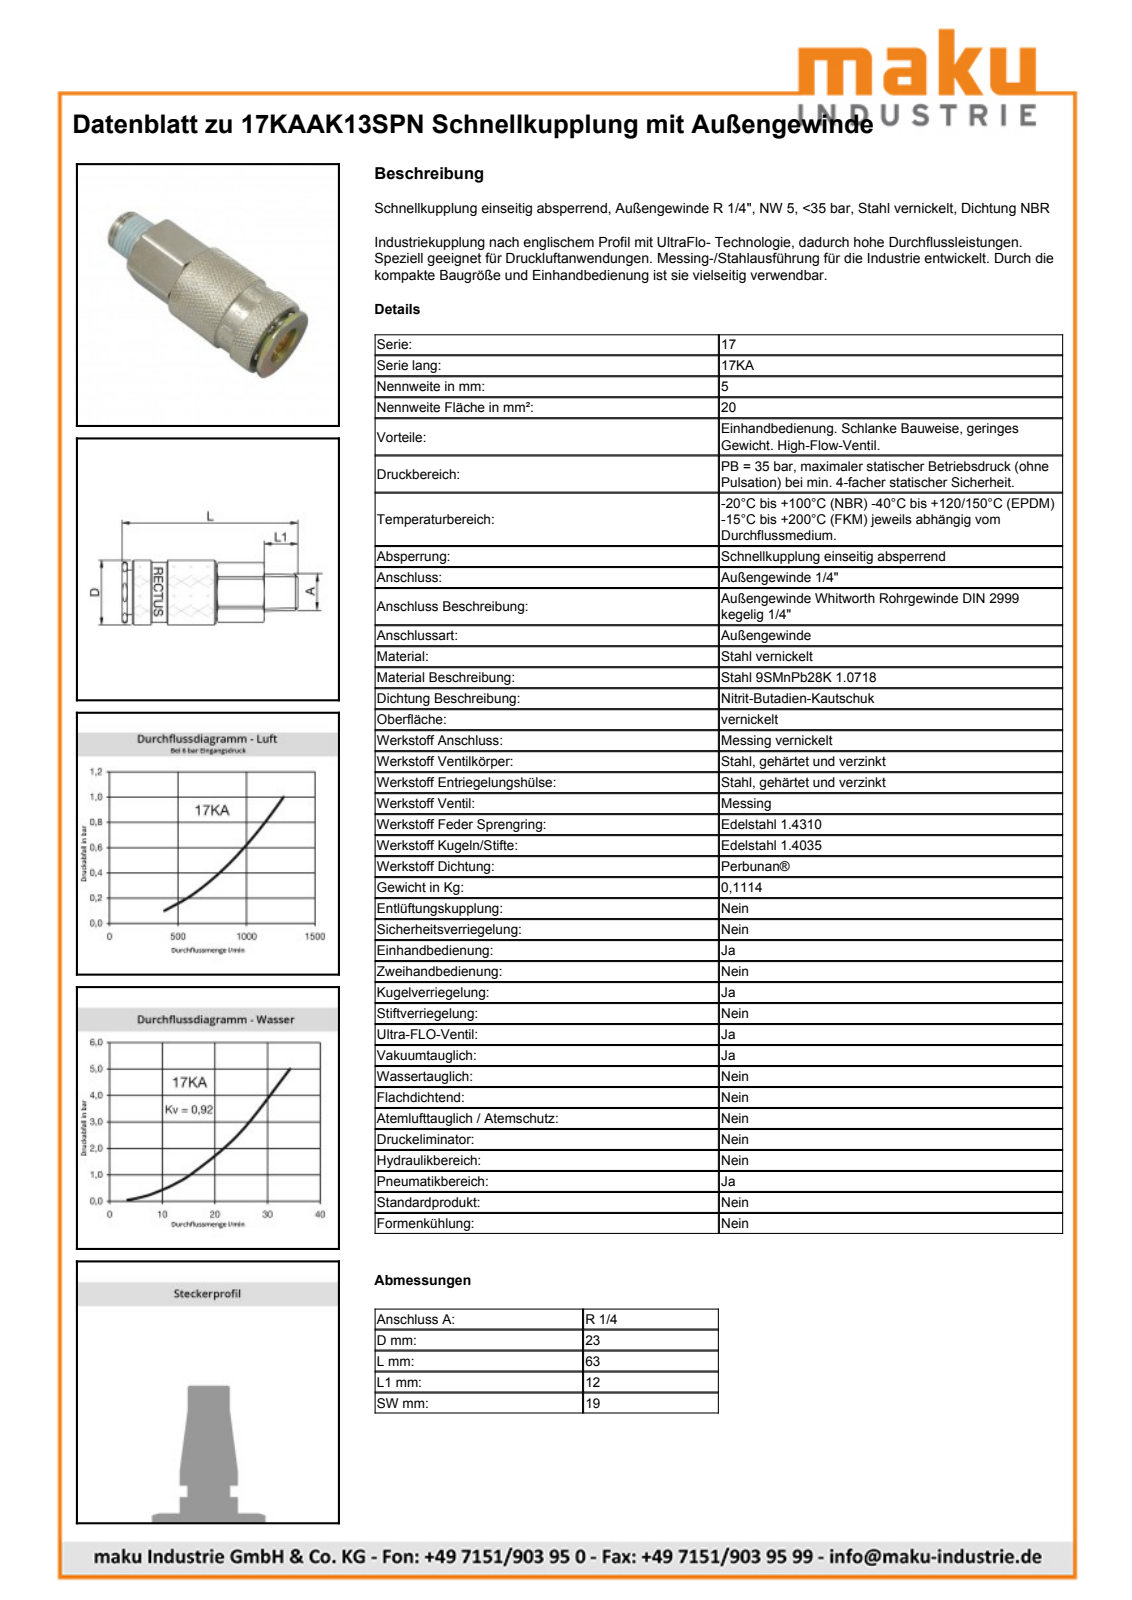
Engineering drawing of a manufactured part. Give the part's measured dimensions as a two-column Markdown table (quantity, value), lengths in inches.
| quantity | value |
| --- | --- |
| part name | D108262 |
| STEP written by | Autodesk Inventor 2013 (AUTOMOTIVE_DESIGN) |
| units | inches |
| bodies | 2 solids, 525 faces (214 planar, 67 cylindrical, 244 other) |
| overall size | 2.484 × 0.911 × 0.911 |
| volume | 1.189 in³ |
| surface area | 14.11 in² |
| round holes (diameter × count) | 0.594 × 1, 0.609 × 1, 0.636 × 1, 0.73 × 1, 0.758 × 1 |
| round bosses / shafts (diameter × count) | 0.911 × 1, 0.846 × 1, 0.746 × 1, 0.63 × 1, 0.602 × 1, 0.591 × 1, 0.572 × 1 |
| partial cylindrical surfaces (radius × count) | 0.419 × 1, 0.421 × 1, 0.433 × 1 |
| main face-to-face distances | 0.748, 0.071, 0.256, 2.012, 0.142, 1.87, 2.484, 2.343, 0.472, 1.941 |
